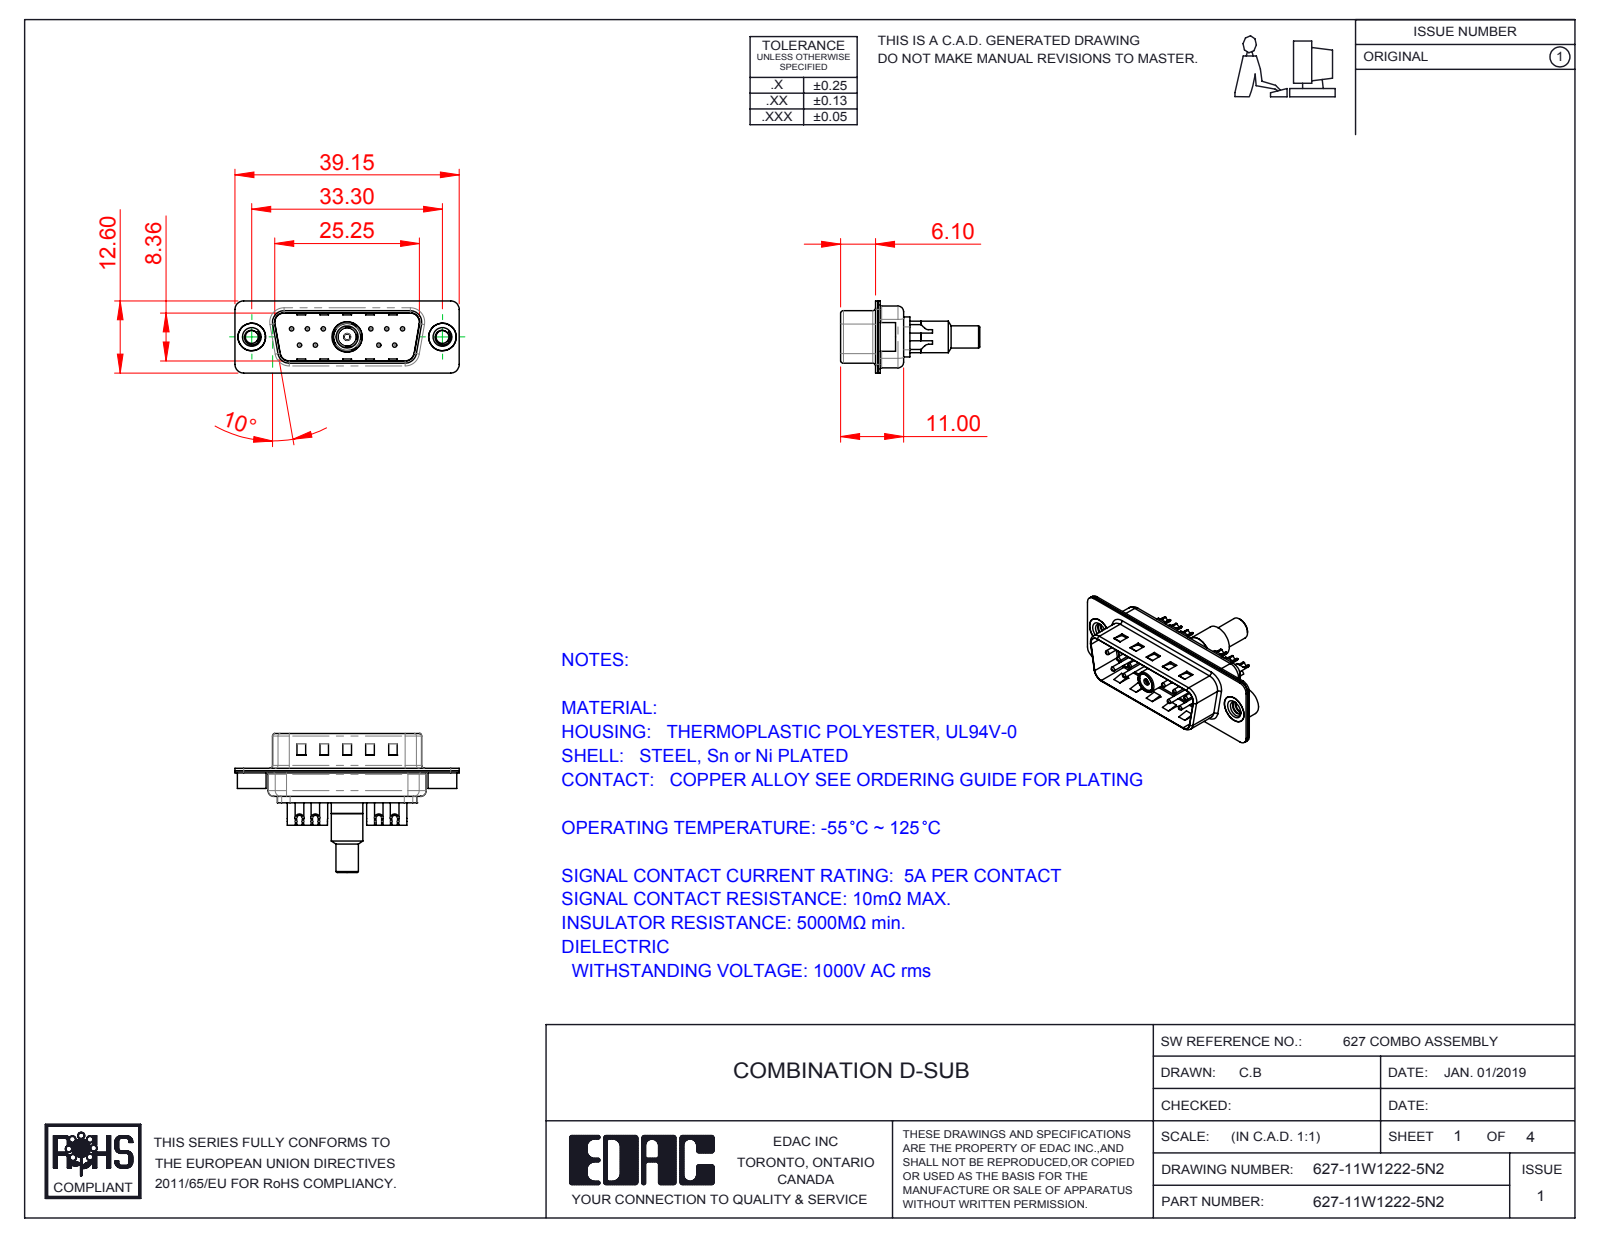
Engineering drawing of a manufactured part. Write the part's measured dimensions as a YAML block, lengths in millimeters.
part_name: "Co-Ax Jack Assy_SC; Solder Cover; Socket_Solder Cup; Locking Collar (+8 more)"
step_written_by: "SolidWorks 2016 (CONFIG_CONTROL_DESIGN)"
units: millimeters
bodies: {solids: 21, faces: 853, planar: 278, cylindrical: 361, other: 214}
overall_size: [39.15, 24.3, 12.6]
volume: 1985
surface_area: 5705
round_holes:
  - {diameter: 1.6, count: 11}
  - {diameter: 0.75, count: 10}
  - {diameter: 1, count: 10}
  - {diameter: 2, count: 10}
  - {diameter: 4.8, count: 3}
  - {diameter: 2.26, count: 2}
  - {diameter: 4, count: 2}
  - {diameter: 0.8, count: 1}
  - {diameter: 1.1, count: 1}
  - {diameter: 1.2, count: 1}
  - {diameter: 1.5, count: 1}
  - {diameter: 1.8, count: 1}
round_bosses_or_shafts:
  - {diameter: 1.5, count: 10}
  - {diameter: 5, count: 2}
  - {diameter: 4.9, count: 2}
  - {diameter: 5.5, count: 1}
  - {diameter: 5.2, count: 1}
  - {diameter: 4.75, count: 1}
  - {diameter: 4.73, count: 1}
  - {diameter: 3.9, count: 1}
partial_cylinders:
  - {radius: 1.5, count: 21}
  - {radius: 2, count: 12}
  - {radius: 1, count: 9}
  - {radius: 0.5, count: 8}
  - {radius: 1.6, count: 8}
  - {radius: 0.25, count: 4}
  - {radius: 0.6, count: 4}
  - {radius: 0.65, count: 4}
face_to_face_distances: [0.4, 0.82, 9.58, 8.76, 0.8, 1.5, 6, 1.4, 5.2, 5.6]
hole_center_spacings: [3.16, 2.77, 13.85, 11.08, 16.62, 5.03, 5.04, 5.54]
